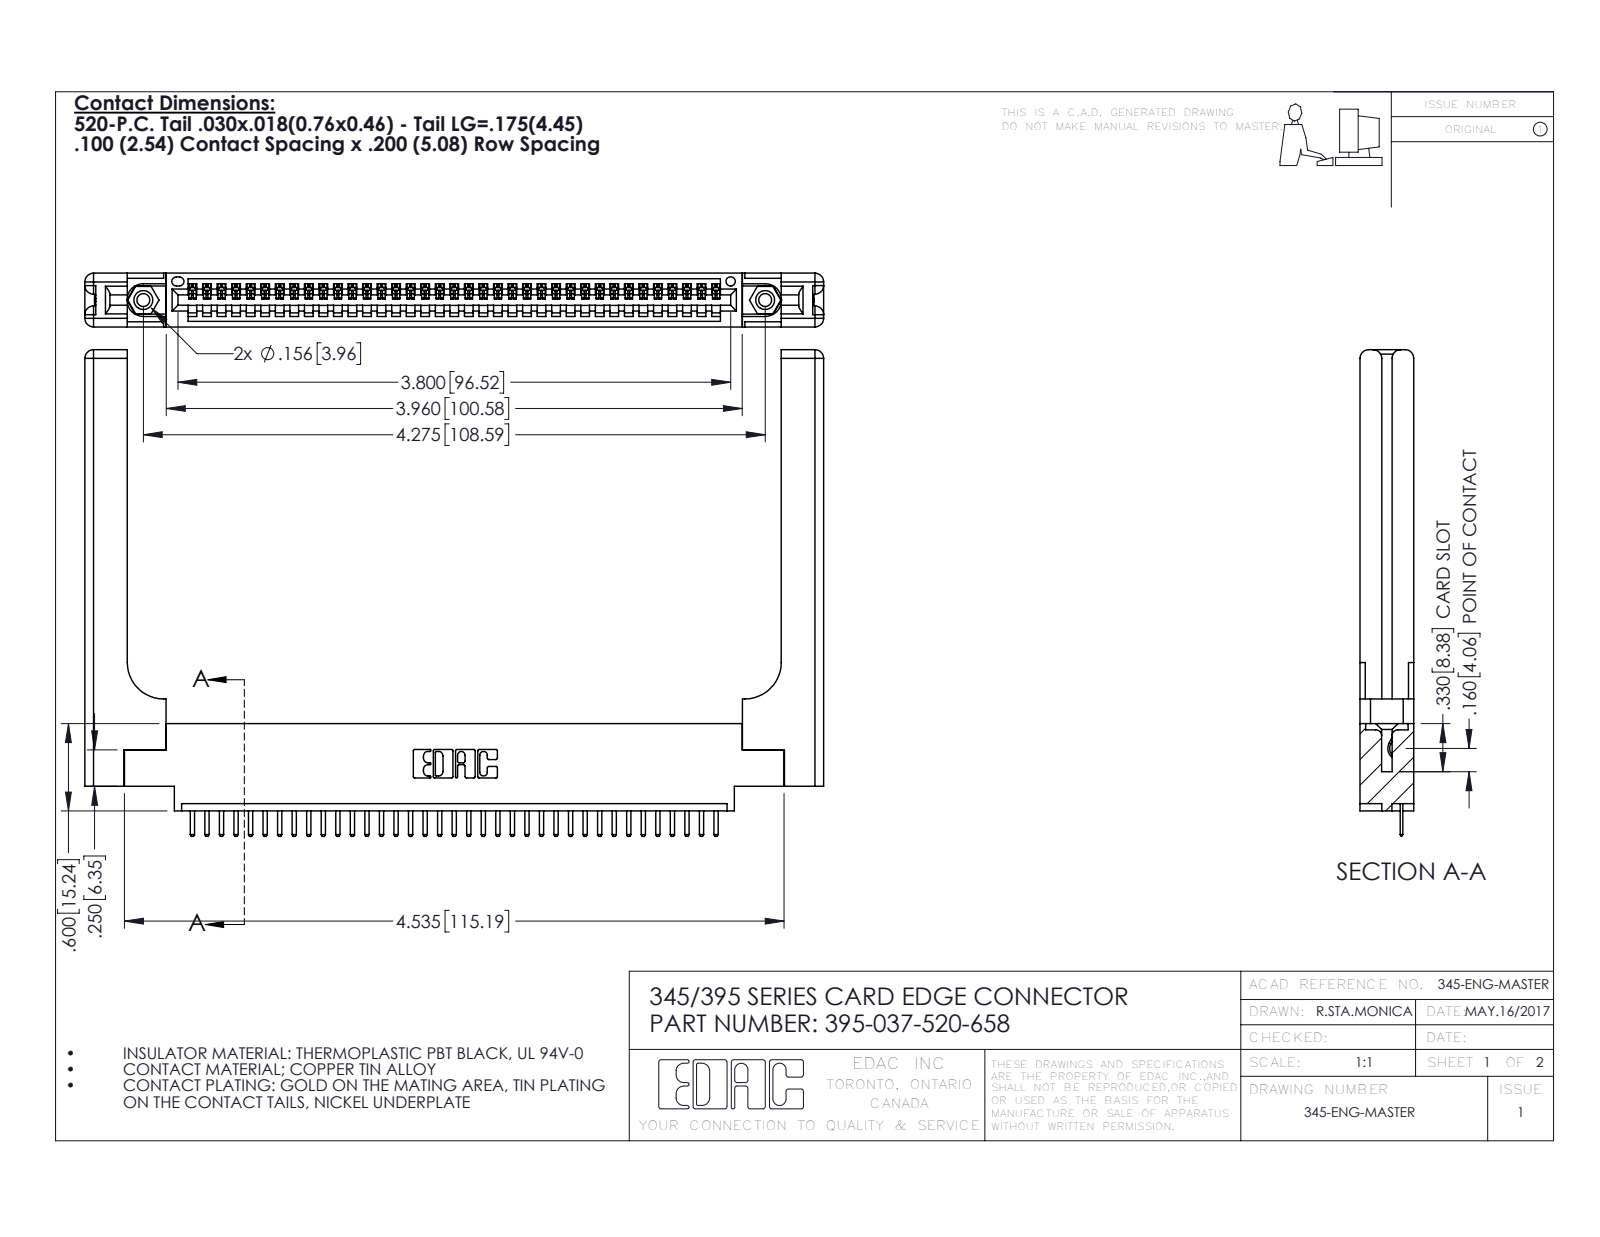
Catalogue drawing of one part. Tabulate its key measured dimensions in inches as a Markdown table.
| quantity | value |
| --- | --- |
| part name | 345 Part_0.170 Offset - 0.156 Dia-TH; 395-037-520-658; 345-220-058_345-220-058; 345-250-001_345-250-001-102 (+1 more) |
| STEP written by | SolidWorks 2016 (CONFIG_CONTROL_DESIGN) |
| units | inches |
| bodies | 42 solids, 2680 faces (1786 planar, 834 cylindrical, 60 other) |
| overall size | 5.079 × 3.345 × 0.37 |
| volume | 1.251 in³ |
| surface area | 32.48 in² |
| round holes (diameter × count) | 0.089 × 2, 0.125 × 2, 0.156 × 2, 0.064 × 1 |
| round bosses / shafts (diameter × count) | 0.155 × 2 |
| partial cylindrical surfaces (radius × count) | 0.01 × 76, 0.006 × 74, 0.01 × 22, 0.06 × 16, 0.007 × 6, 0.031 × 6, 0.026 × 3, 0.03 × 2 |
| main face-to-face distances | 0.37, 0.072, 0.298, 0.098, 0.272, 0.025, 0.2, 0.148, 0.15, 0.225 |
| hole center spacings | 0.27, 4.039, 4.275 |
